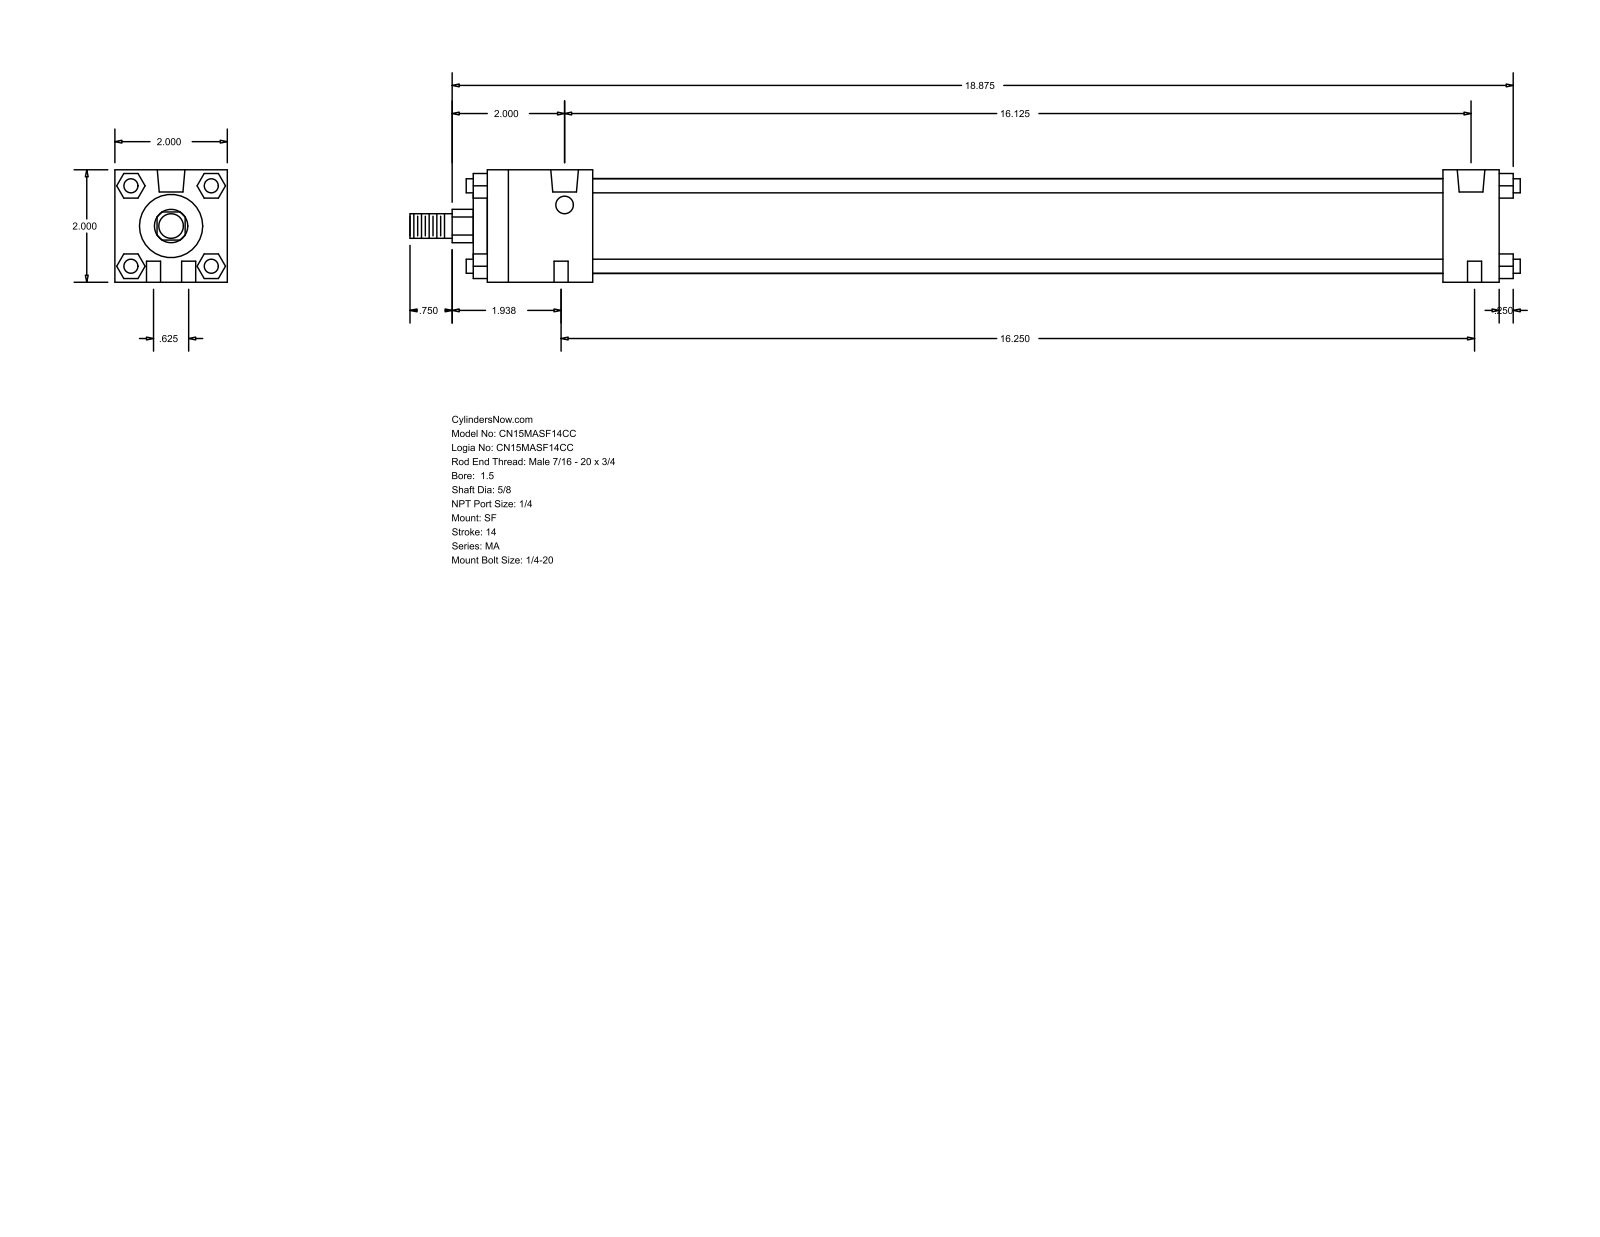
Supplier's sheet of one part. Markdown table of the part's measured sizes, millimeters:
| quantity | value |
| --- | --- |
| part name | MA_SF__0150_0.625 |
| STEP written by | GSSL Pune (CONFIG_CONTROL_DESIGN) |
| units | millimeters |
| bodies | 0 solids, 124 faces (94 planar, 30 cylindrical, 0 other) |
| overall size | 501.65 × 50.8 × 50.8 |
| round holes (diameter × count) | 6.35 × 4, 7.94 × 2, 12.49 × 2 |
| round bosses / shafts (diameter × count) | 6.35 × 4, 42.93 × 1, 28.57 × 1, 15.88 × 1, 11.11 × 1 |
| partial cylindrical surfaces (radius × count) | 7.54 × 1 |
| main face-to-face distances | 50.8, 457.19, 47.62, 431.8, 384.18, 409.57, 25.39, 6.35, 53.97, 438.15 |
| hole center spacings | 8.1, 15.88, 409.58, 411.24, 411.25, 412.75, 413.06 |
